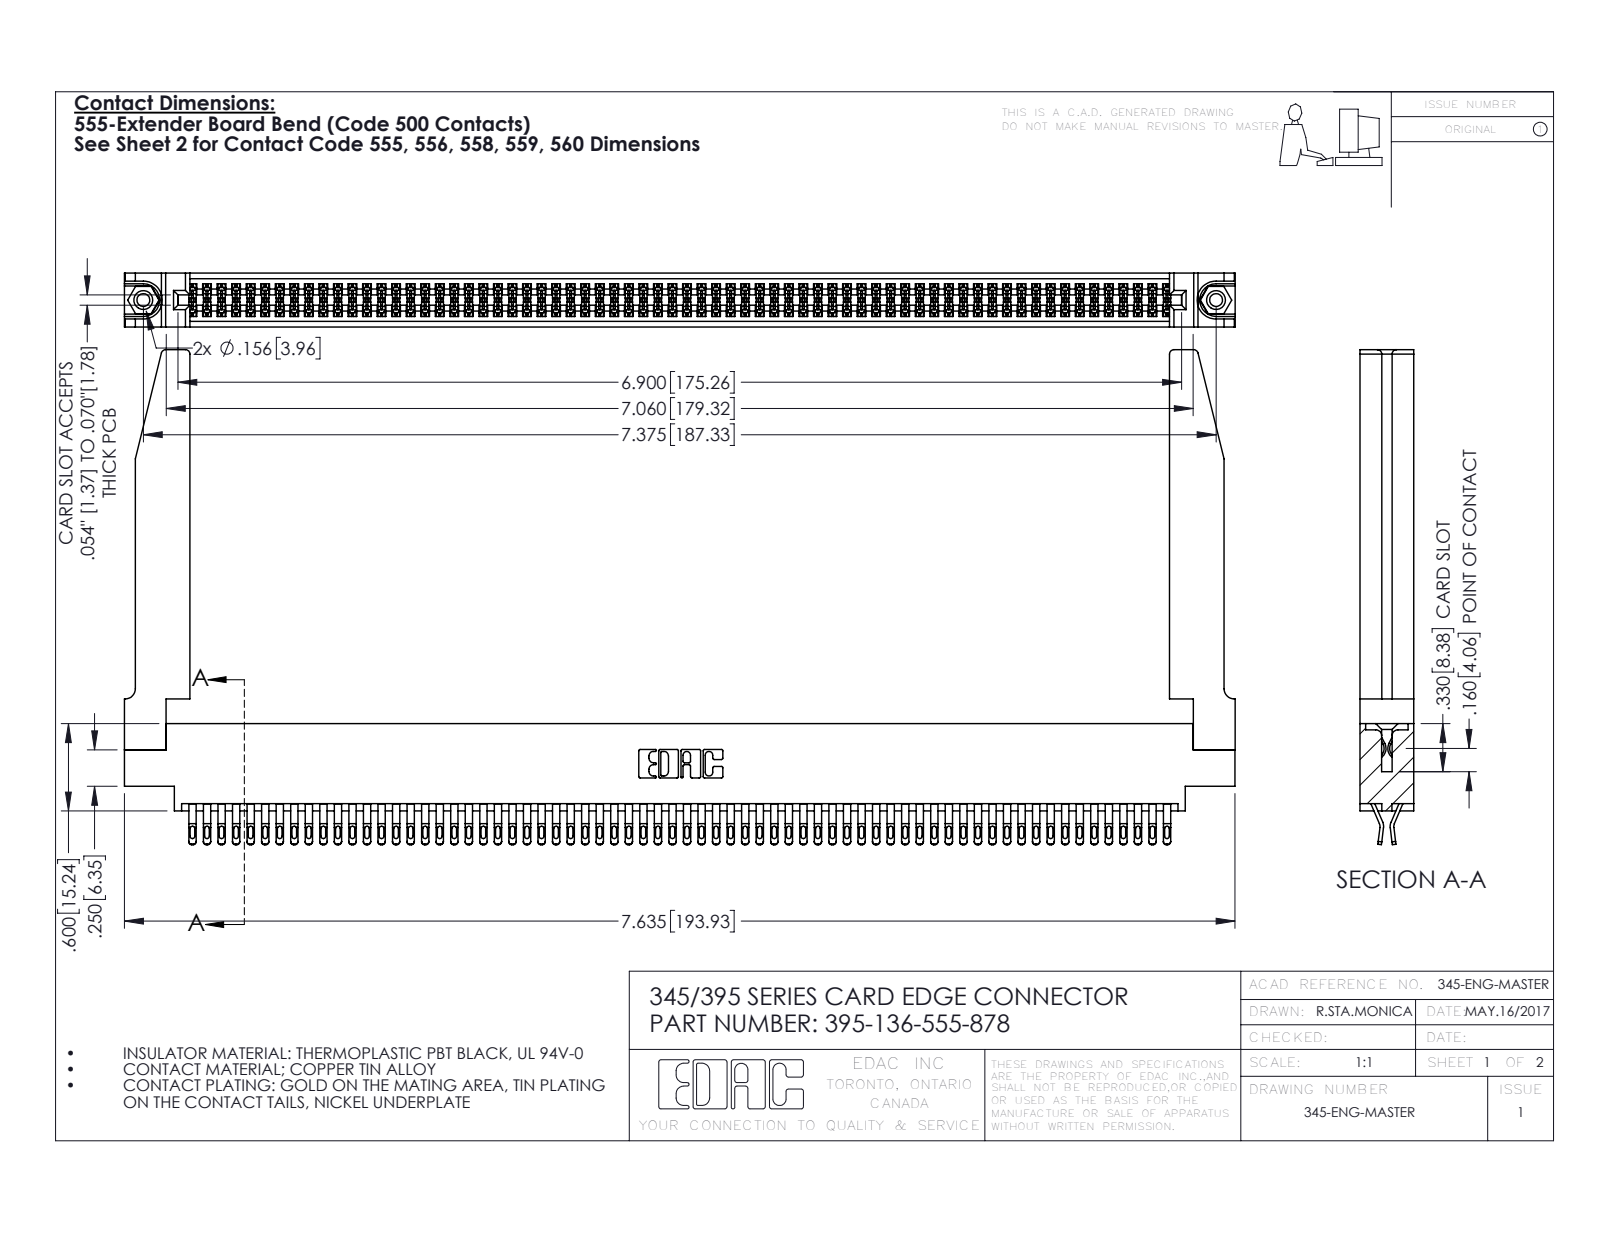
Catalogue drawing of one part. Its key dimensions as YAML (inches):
part_name: "345-220-078_345-220-078; 395-136-555-878; 345-292-001_555 Tail; 345-250-001_345-250-001-102 (+1 more)"
step_written_by: "SolidWorks 2016 (CONFIG_CONTROL_DESIGN)"
units: inches
bodies: {solids: 141, faces: 7980, planar: 4442, cylindrical: 3486, other: 52}
overall_size: [7.636, 3.402, 0.37]
volume: 1.656
surface_area: 58.09
round_holes:
  - {diameter: 0.089, count: 2}
  - {diameter: 0.125, count: 2}
  - {diameter: 0.156, count: 2}
  - {diameter: 0.064, count: 1}
round_bosses_or_shafts:
  - {diameter: 0.155, count: 2}
partial_cylinders:
  - {radius: 0.016, count: 340}
  - {radius: 0.02, count: 272}
  - {radius: 0.006, count: 204}
  - {radius: 0.01, count: 22}
  - {radius: 0.03, count: 8}
  - {radius: 0.007, count: 6}
  - {radius: 0.031, count: 6}
  - {radius: 0.026, count: 3}
face_to_face_distances: [0.072, 0.37, 0.298, 0.025, 0.098, 0.272, 0.2, 0.225, 0.175, 0.149]
hole_center_spacings: [0.27, 7.139, 7.375]
